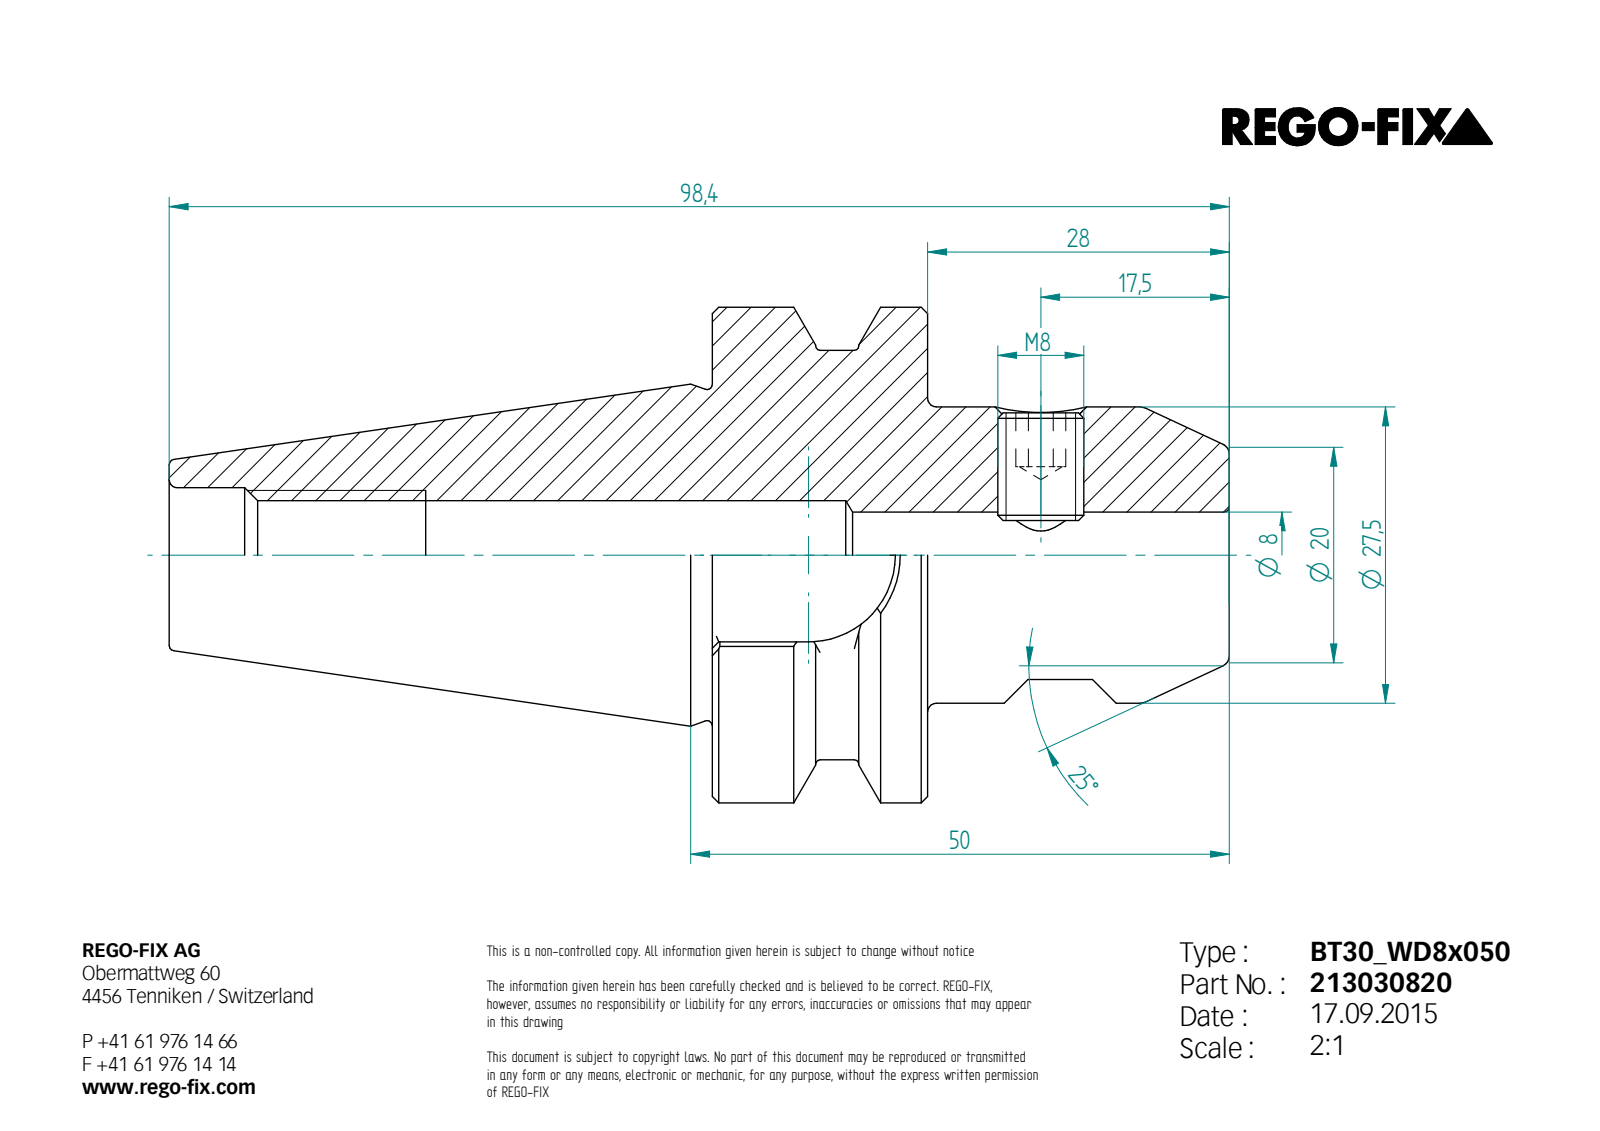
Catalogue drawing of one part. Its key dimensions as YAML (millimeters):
step_written_by: "Unknown (AUTOMOTIVE_DESIGN)"
units: millimeters
bodies: {solids: 2, faces: 104, planar: 47, cylindrical: 22, other: 35}
overall_size: [98.4, 46, 46]
volume: 61204
surface_area: 15476
round_holes:
  - {diameter: 6.65, count: 1}
  - {diameter: 8, count: 1}
  - {diameter: 10.11, count: 1}
  - {diameter: 12.5, count: 1}
round_bosses_or_shafts:
  - {diameter: 46, count: 1}
  - {diameter: 27.5, count: 1}
  - {diameter: 8, count: 1}
partial_cylinders:
  - {radius: 0.5, count: 8}
  - {radius: 8.05, count: 1}
  - {radius: 19, count: 1}
face_to_face_distances: [20, 32.5, 48, 28, 19.6, 3.5, 16.1, 50.4, 70.4, 98.4]
